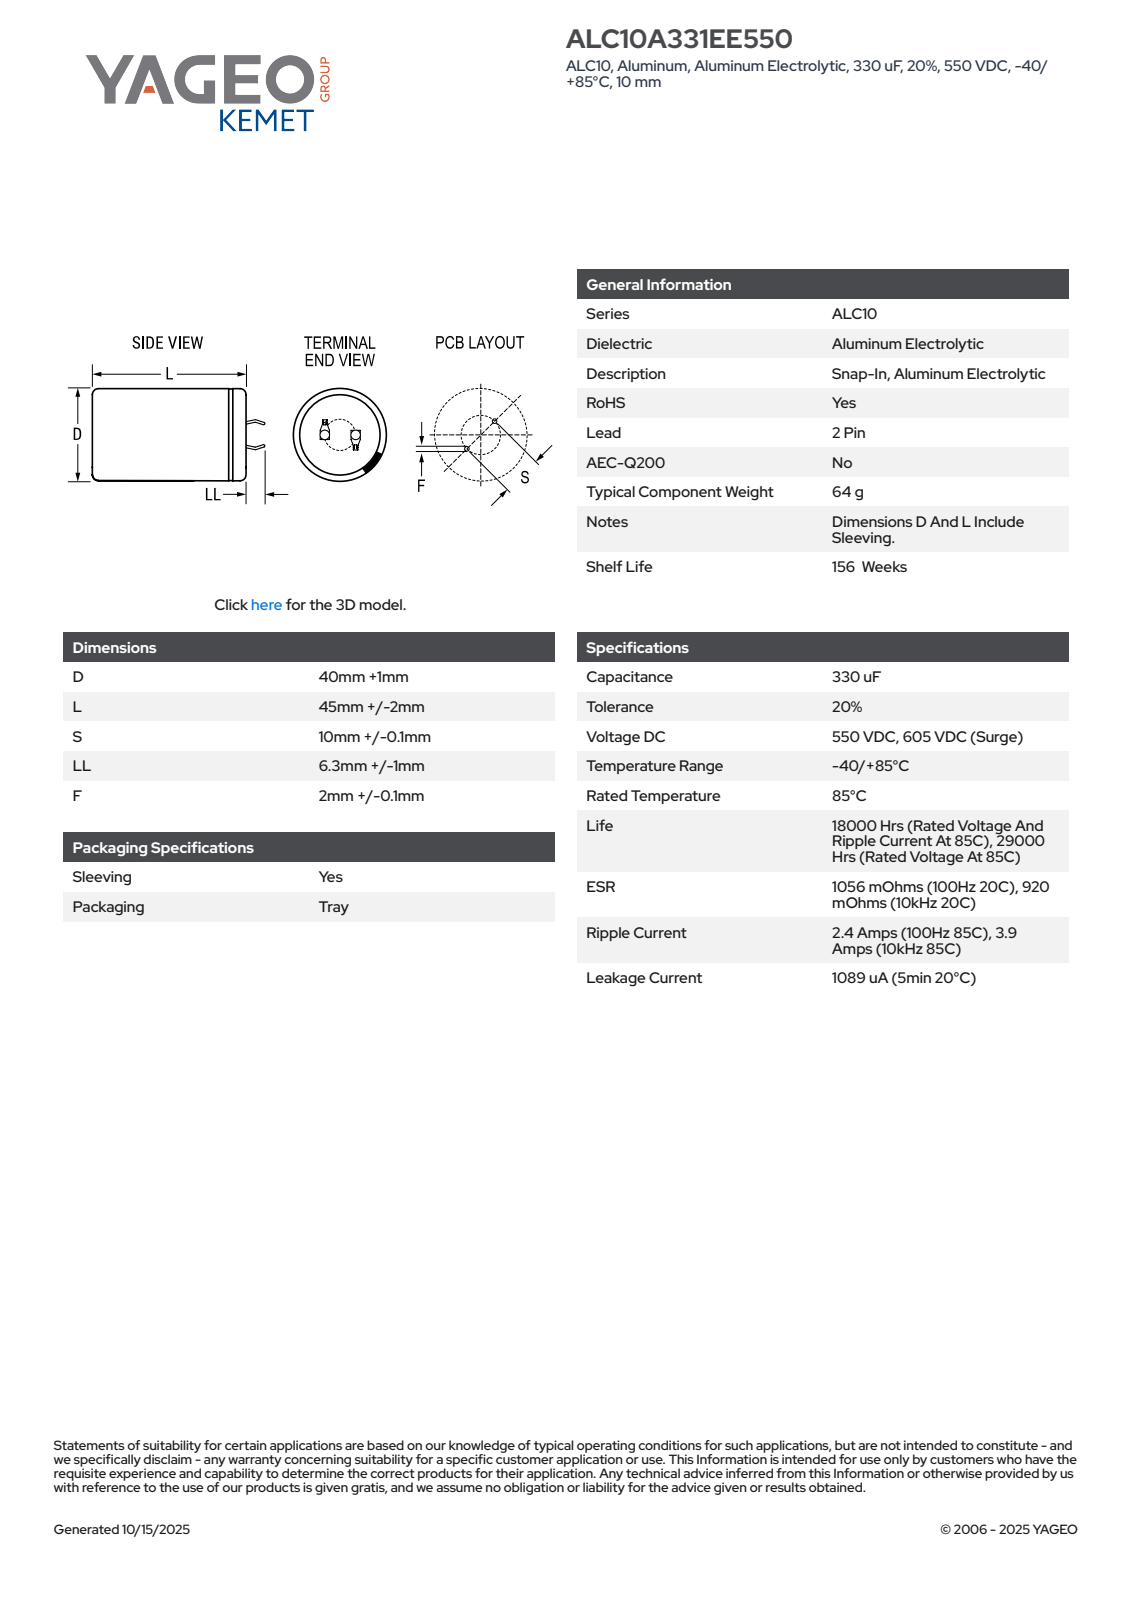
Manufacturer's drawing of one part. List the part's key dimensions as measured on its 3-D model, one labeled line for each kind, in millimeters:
Part name (STEP PRODUCT): CARS_K2P_40X45_D41L47S10LL7.3F2.1
STEP written by: SolidWorks 2014 (AUTOMOTIVE_DESIGN)
Units: millimetres
Bodies: 1 solid, 100 faces (52 planar, 9 cylindrical, 39 other)
Overall size (bounding box): 54.29 × 41 × 41
Volume: 61 267 mm³ · Surface area: 8 677 mm²
Round holes (diameter × count): ⌀36.28 ×1
Round bosses / shafts (diameter × count): ⌀41 ×1
Partial cylindrical surfaces — rounded edges, fillets, slot ends (radius × count): R20.49 ×1
Main face-to-face distances: 46.99, 0.6, 47.49, 0.5, 7.08, 7.64, 0.75, 1.35, 7.68, 6.48
